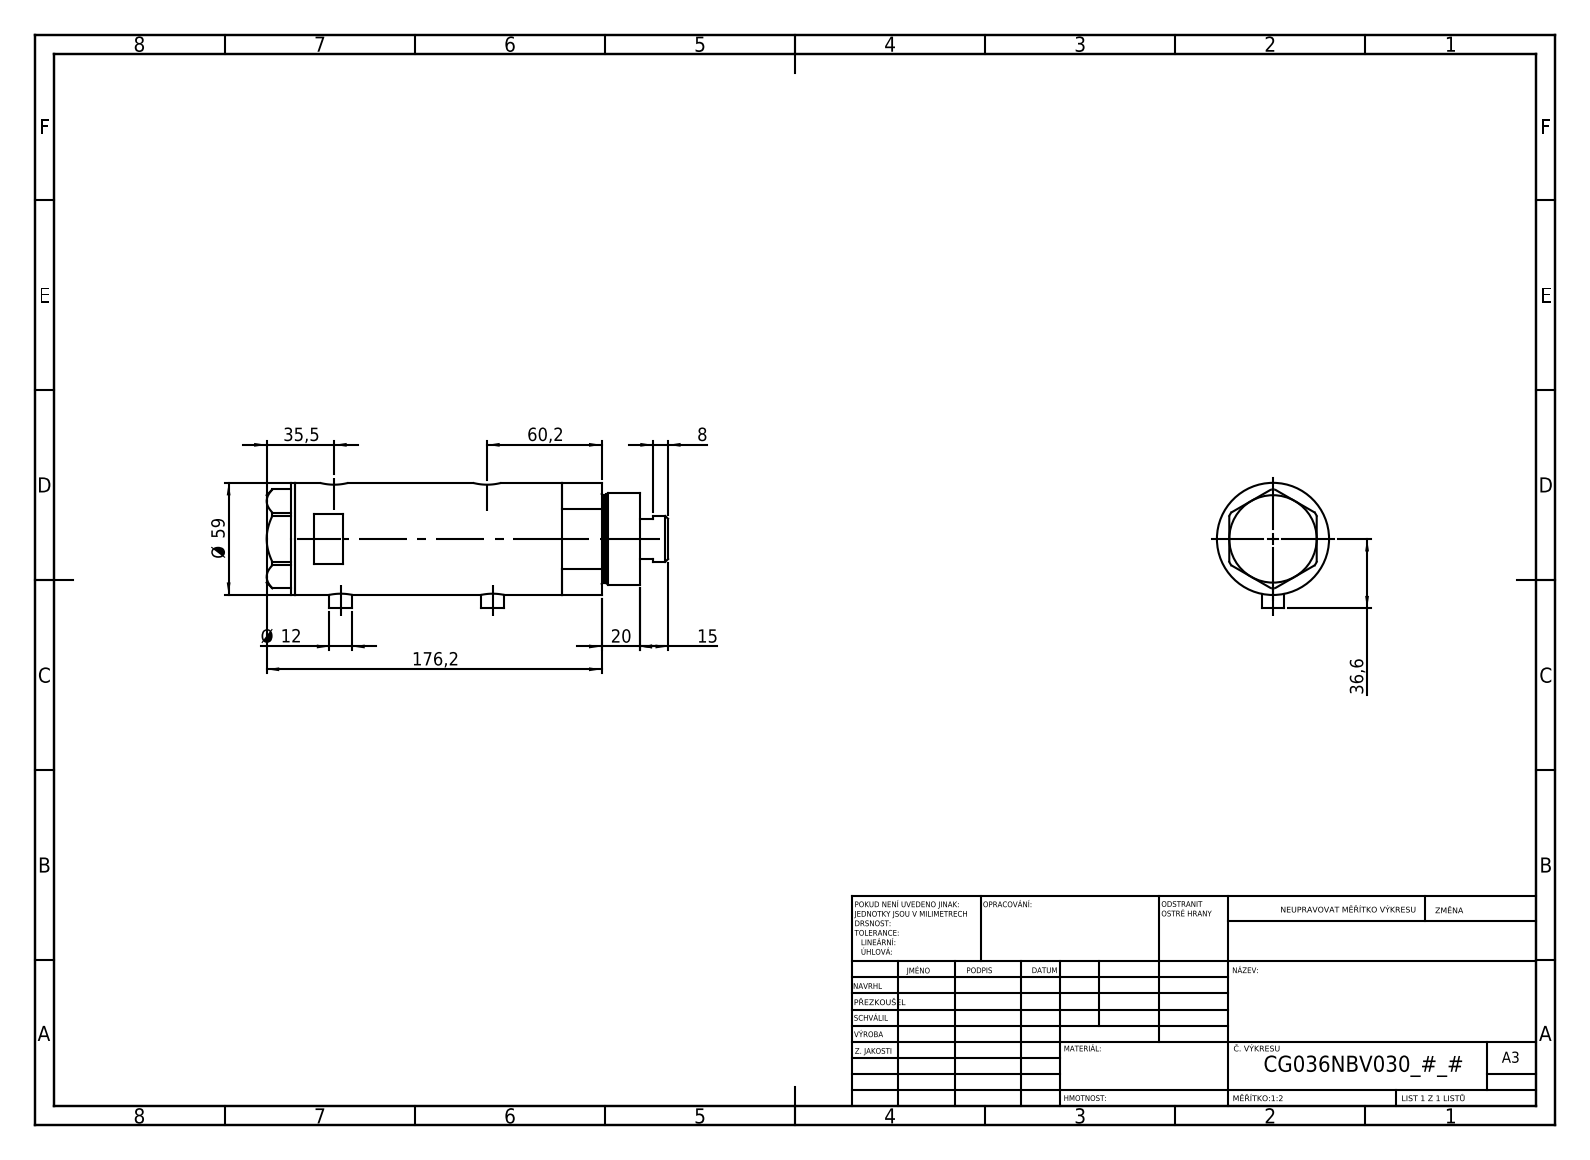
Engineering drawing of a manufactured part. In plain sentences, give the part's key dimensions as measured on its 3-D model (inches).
The part is named "V270CG_VC; V270CG_MIDDLE; V270CG_BACK; V270CG_FRONT". Its 3-D file was written by "SolidWorks 2019 (CONFIG_CONTROL_DESIGN)". It is 4 solids with 120 faces: 51 planar, 49 cylindrical and 20 other. Overall it measures 8.315 by 2.602 by 2.323 inches. Its volume is 29.84 cubic inches and its surface area 156 square inches. Round holes: 2 of diameter 0.383, 2 of diameter 0.492, 2 of diameter 0.591, 1 of diameter 0.335, 1 of diameter 0.984, 1 of diameter 1.043, 1 of diameter 1.417, 1 of diameter 1.575, 1 of diameter 2.047. Round bosses or shafts: 2 of diameter 0.472, 1 of diameter 2.323, 1 of diameter 1.89, 1 of diameter 1.811, 1 of diameter 0.945. The main face-to-face distances are 4.024, 0.925, 3.098, 0.591, 1.516, 4.614, 0.079, 7.724, 7.134, 6.209. The hole center spacings are 0.114, 0.138, 3.031, 3.146, 3.169, 3.283.
